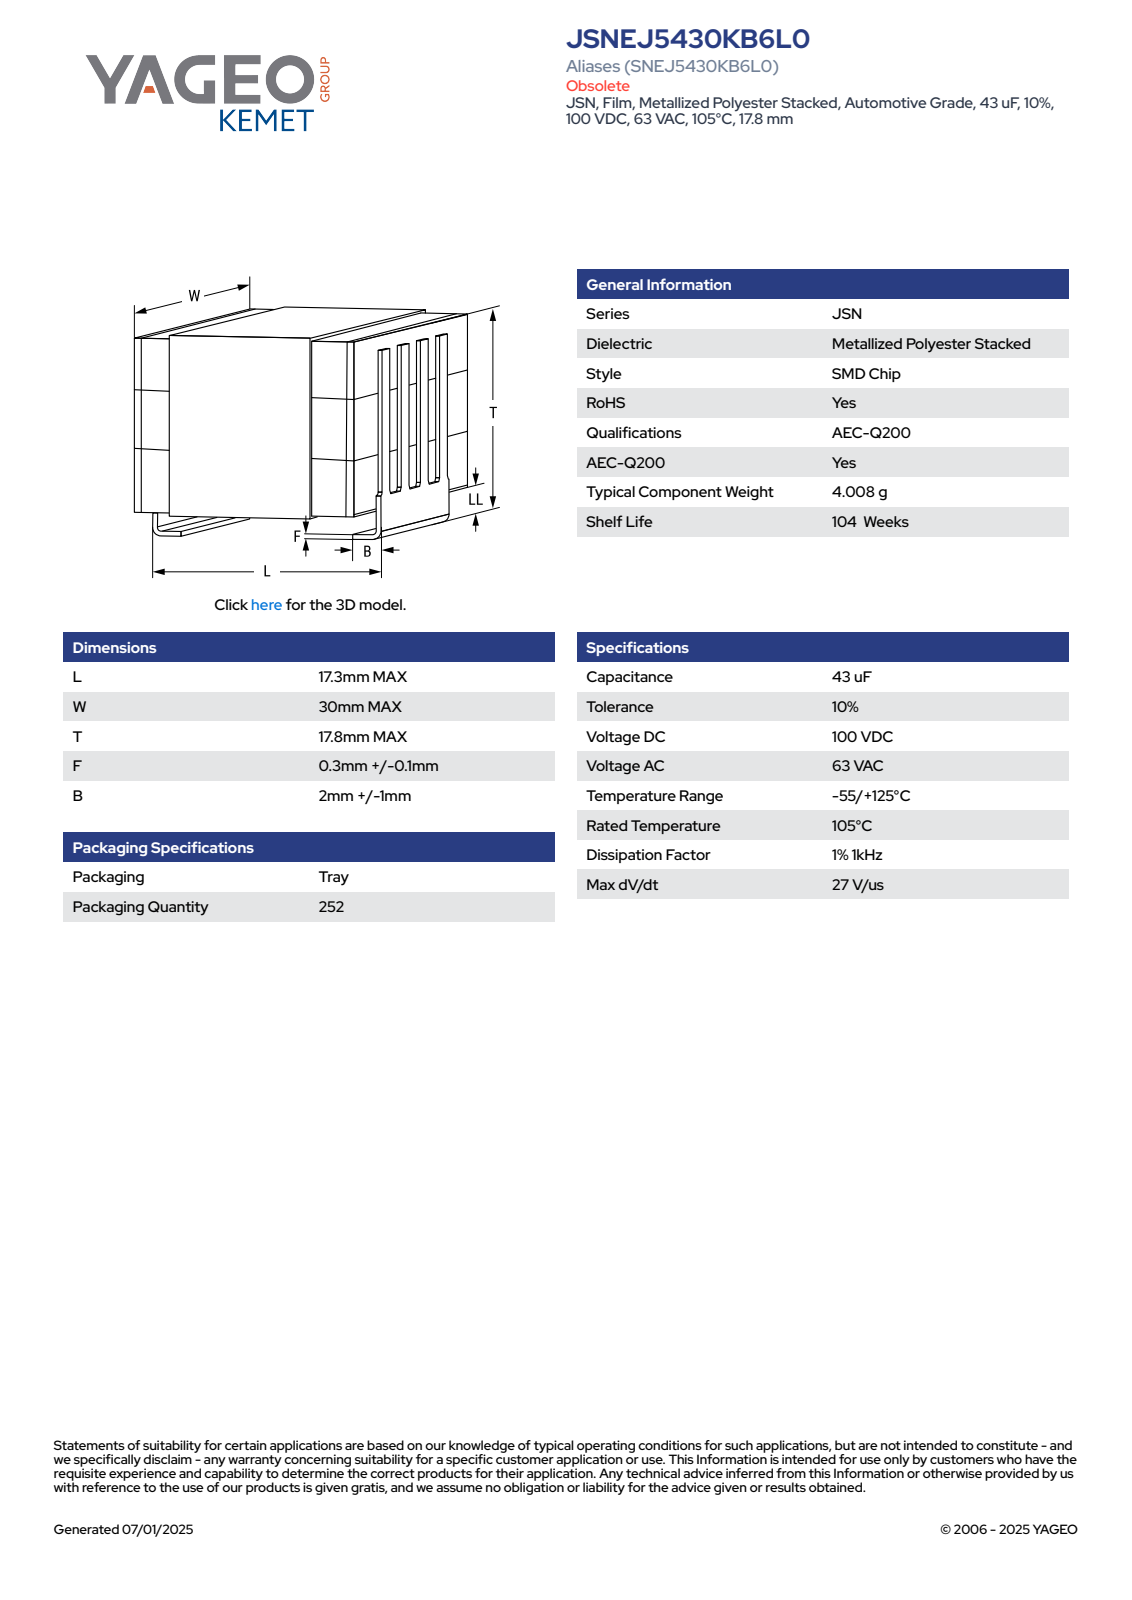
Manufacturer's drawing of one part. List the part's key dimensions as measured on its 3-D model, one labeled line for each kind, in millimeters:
Part name (STEP PRODUCT): CFS_KJSN_L17.3W30T17.8F0.40
STEP written by: SolidWorks 2014 (AUTOMOTIVE_DESIGN)
Units: millimetres
Bodies: 4 solids, 101 faces (97 planar, 4 cylindrical, 0 other)
Overall size (bounding box): 30 × 17.8 × 17.3
Volume: 7 456 mm³ · Surface area: 4 114 mm²
Partial cylindrical surfaces — rounded edges, fillets, slot ends (radius × count): R0.2 ×4
Main face-to-face distances: 4.88, 9.82, 0.4, 9.72, 4.78, 4.94, 16.9, 17.3, 4.98, 9.92
